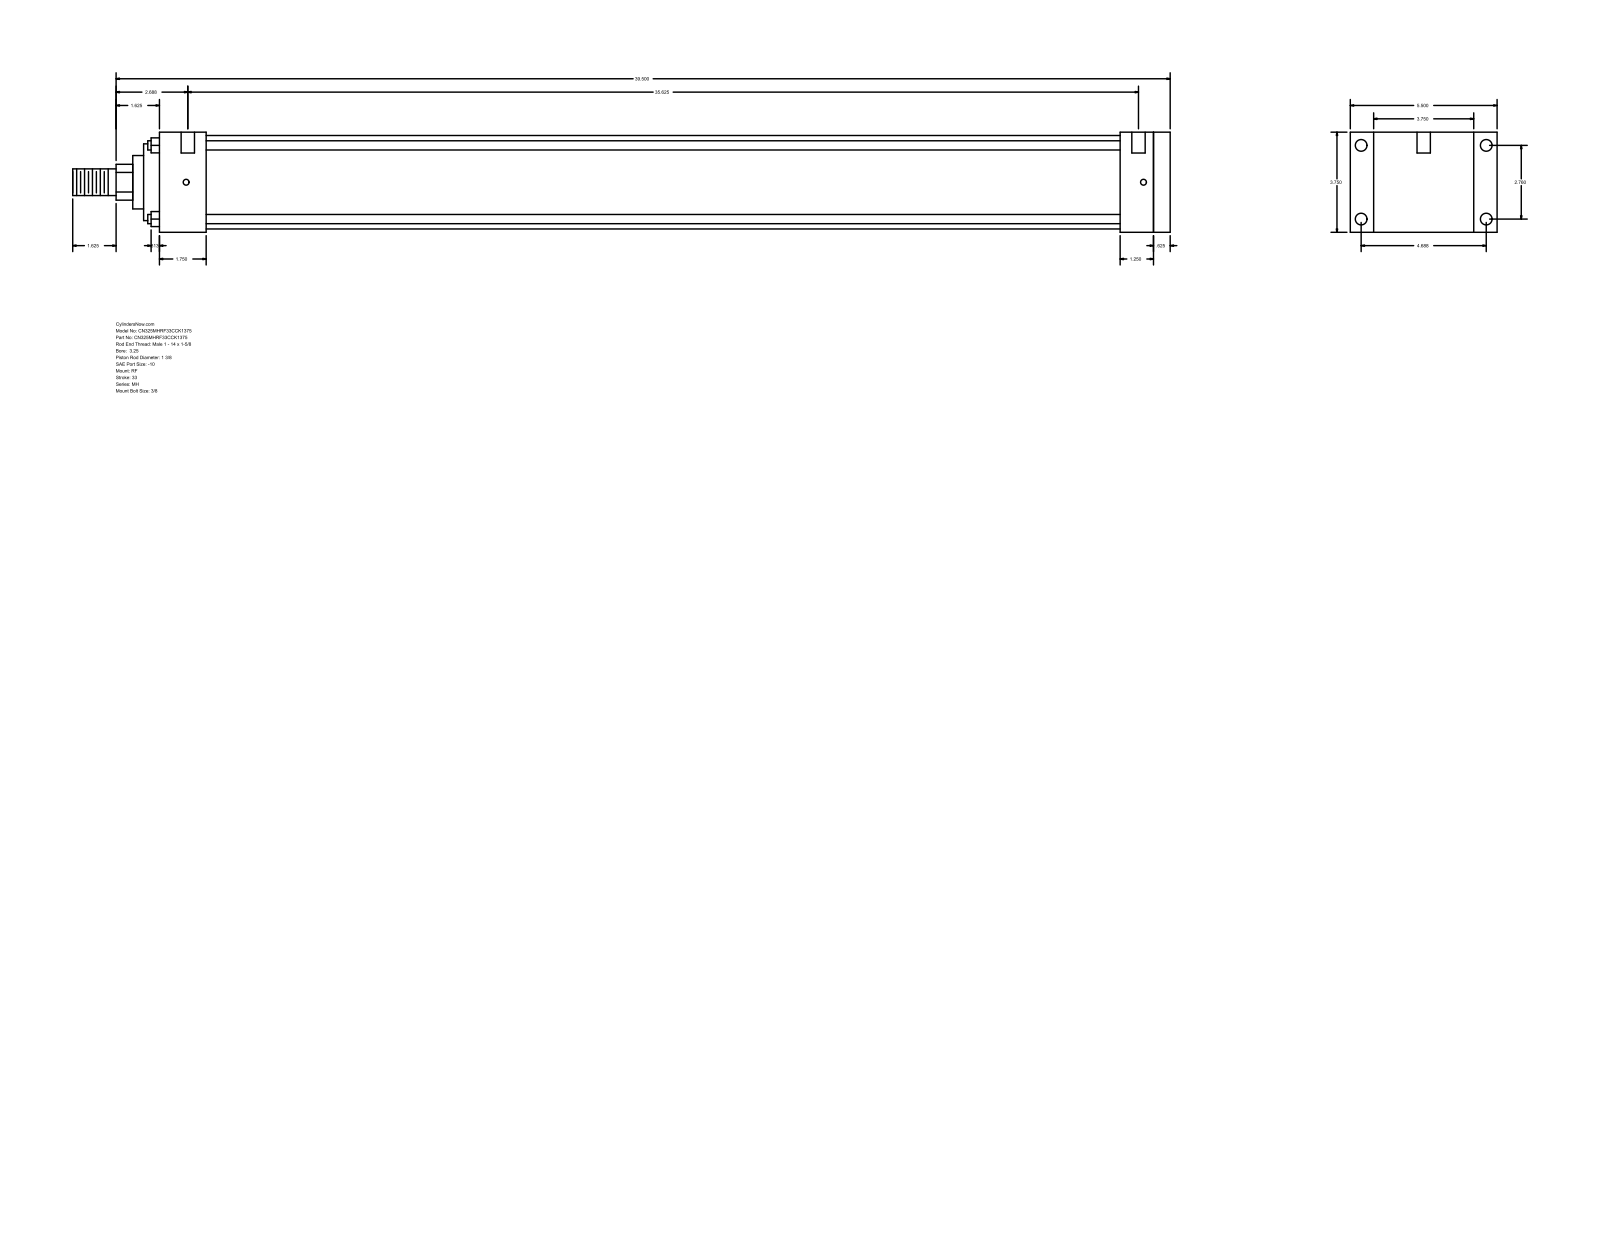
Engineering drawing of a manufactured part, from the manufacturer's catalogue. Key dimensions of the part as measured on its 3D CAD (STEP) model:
Part name (STEP PRODUCT): MH_RF__0325_1.375
STEP written by: GSSL Pune (CONFIG_CONTROL_DESIGN)
Units: millimetres
Bodies: 0 solids, 94 faces (65 planar, 29 cylindrical, 0 other)
Overall size (bounding box): 1044.58 × 139.7 × 95.25
Round holes (diameter × count): ⌀5.56 ×4, ⌀11.13 ×4, ⌀12.7 ×2
Round bosses / shafts (diameter × count): ⌀8.76 ×4, ⌀88.9 ×1, ⌀73.03 ×1, ⌀50.8 ×1, ⌀34.92 ×1, ⌀25.4 ×1
Partial cylindrical surfaces — rounded edges, fillets, slot ends (radius × count): R17.06 ×1
Main face-to-face distances: 95.24, 962.03, 15.88, 946.15, 22.23, 117.47, 44.45, 901.7, 917.58, 914.4
Hole centre spacings: 70.1, 119.06, 138.16, 911.23, 1.59, 4.76, 904.88, 906.47
